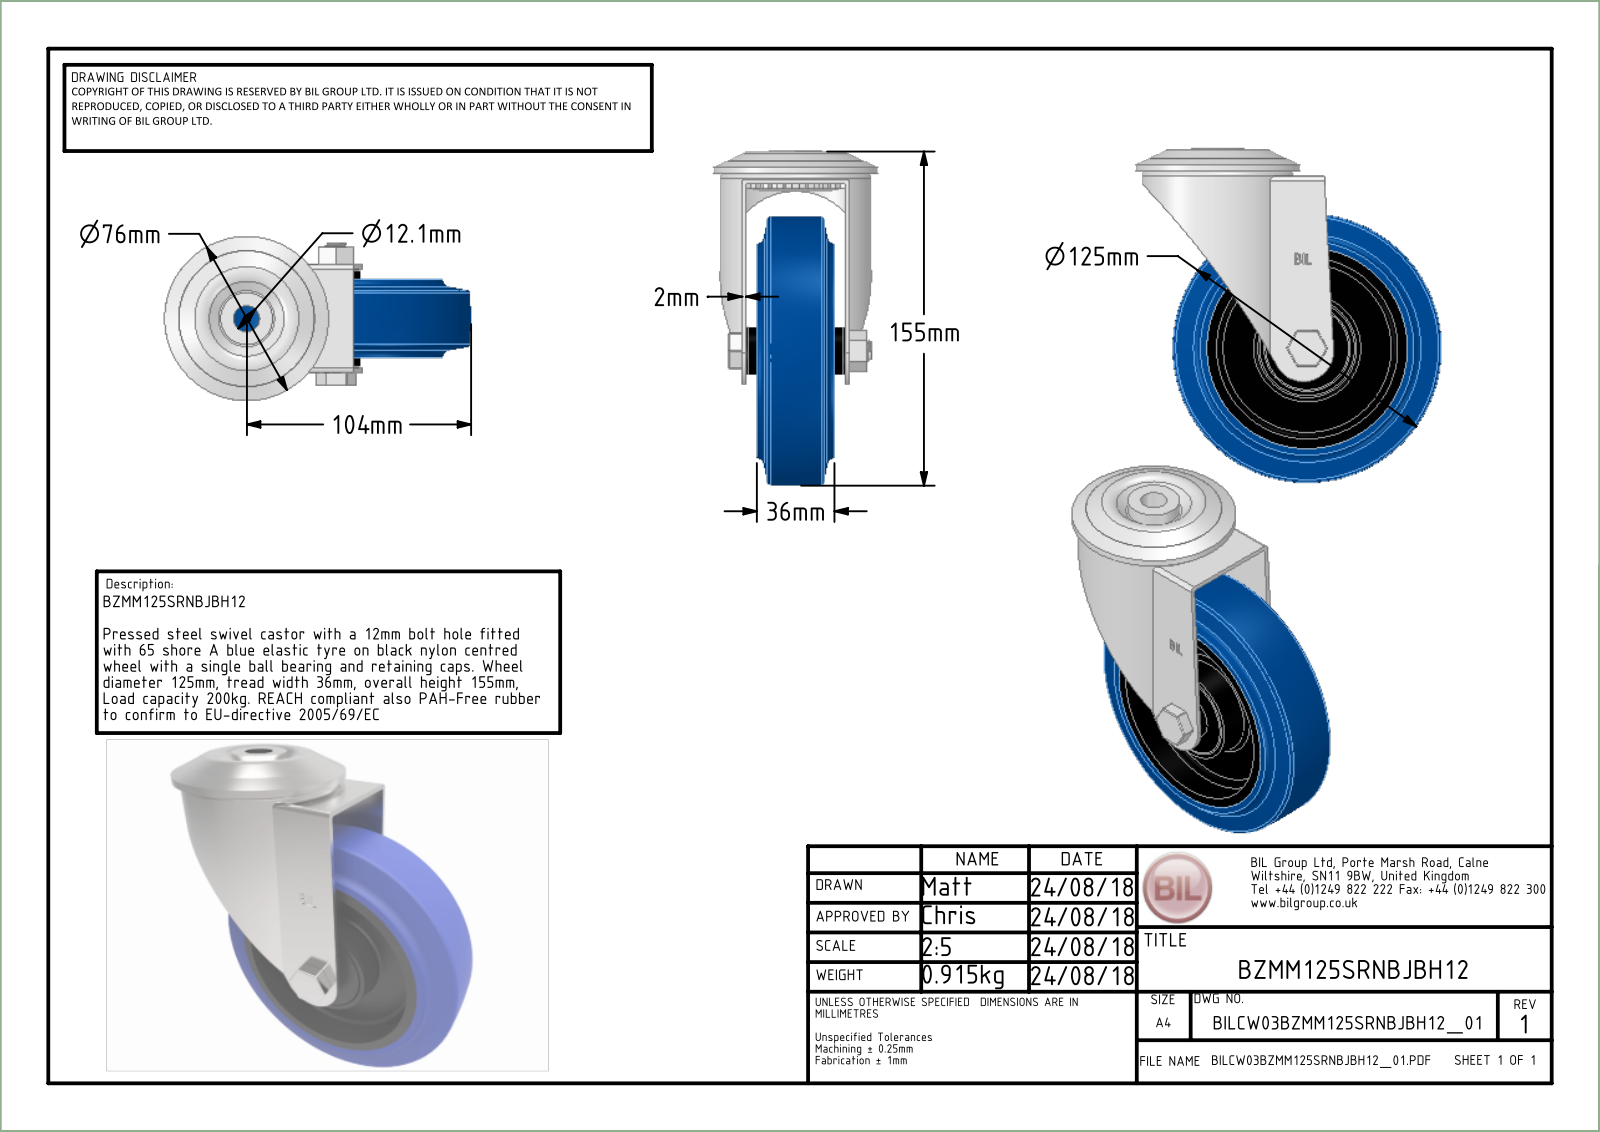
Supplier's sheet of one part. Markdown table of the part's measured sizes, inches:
| quantity | value |
| --- | --- |
| part name | BZMM125SRNBJBH12 v3; BZMM125ASBH12 - 47 v1; ZINC PLATED, PRESSED STEEL HEAD; ZINC PLATED, PRESSED STEEL FORKS (+8 more) |
| STEP written by | Autodesk Translation Framework v13.20.0.188 (AUTOMOTIVE_DESIGN) |
| units | inches |
| bodies | 22 solids, 727 faces (265 planar, 169 cylindrical, 293 other) |
| overall size | 6.102 × 5.591 × 2.992 |
| volume | 19.5 in³ |
| surface area | 225.7 in² |
| round holes (diameter × count) | 0.394 × 1, 0.402 × 1, 0.472 × 1, 0.48 × 1, 0.591 × 1, 0.787 × 1, 0.886 × 1, 0.984 × 1, 1.181 × 1, 1.22 × 1, 1.26 × 1, 1.378 × 1 |
| round bosses / shafts (diameter × count) | 2.756 × 1, 1.949 × 1, 1.713 × 1, 1.506 × 1, 1.496 × 1, 1.358 × 1, 1.201 × 1, 1.093 × 1 |
| partial cylindrical surfaces (radius × count) | 0.02 × 18, 0.03 × 12, 0.049 × 4, 0.098 × 2, 0.472 × 1, 0.531 × 1, 0.541 × 1, 9.985 × 1 |
| main face-to-face distances | 0.098, 0.846, 0.63, 1.102, 1.004, 0.945, 1.949, 0.217, 0.157, 0.315 |
